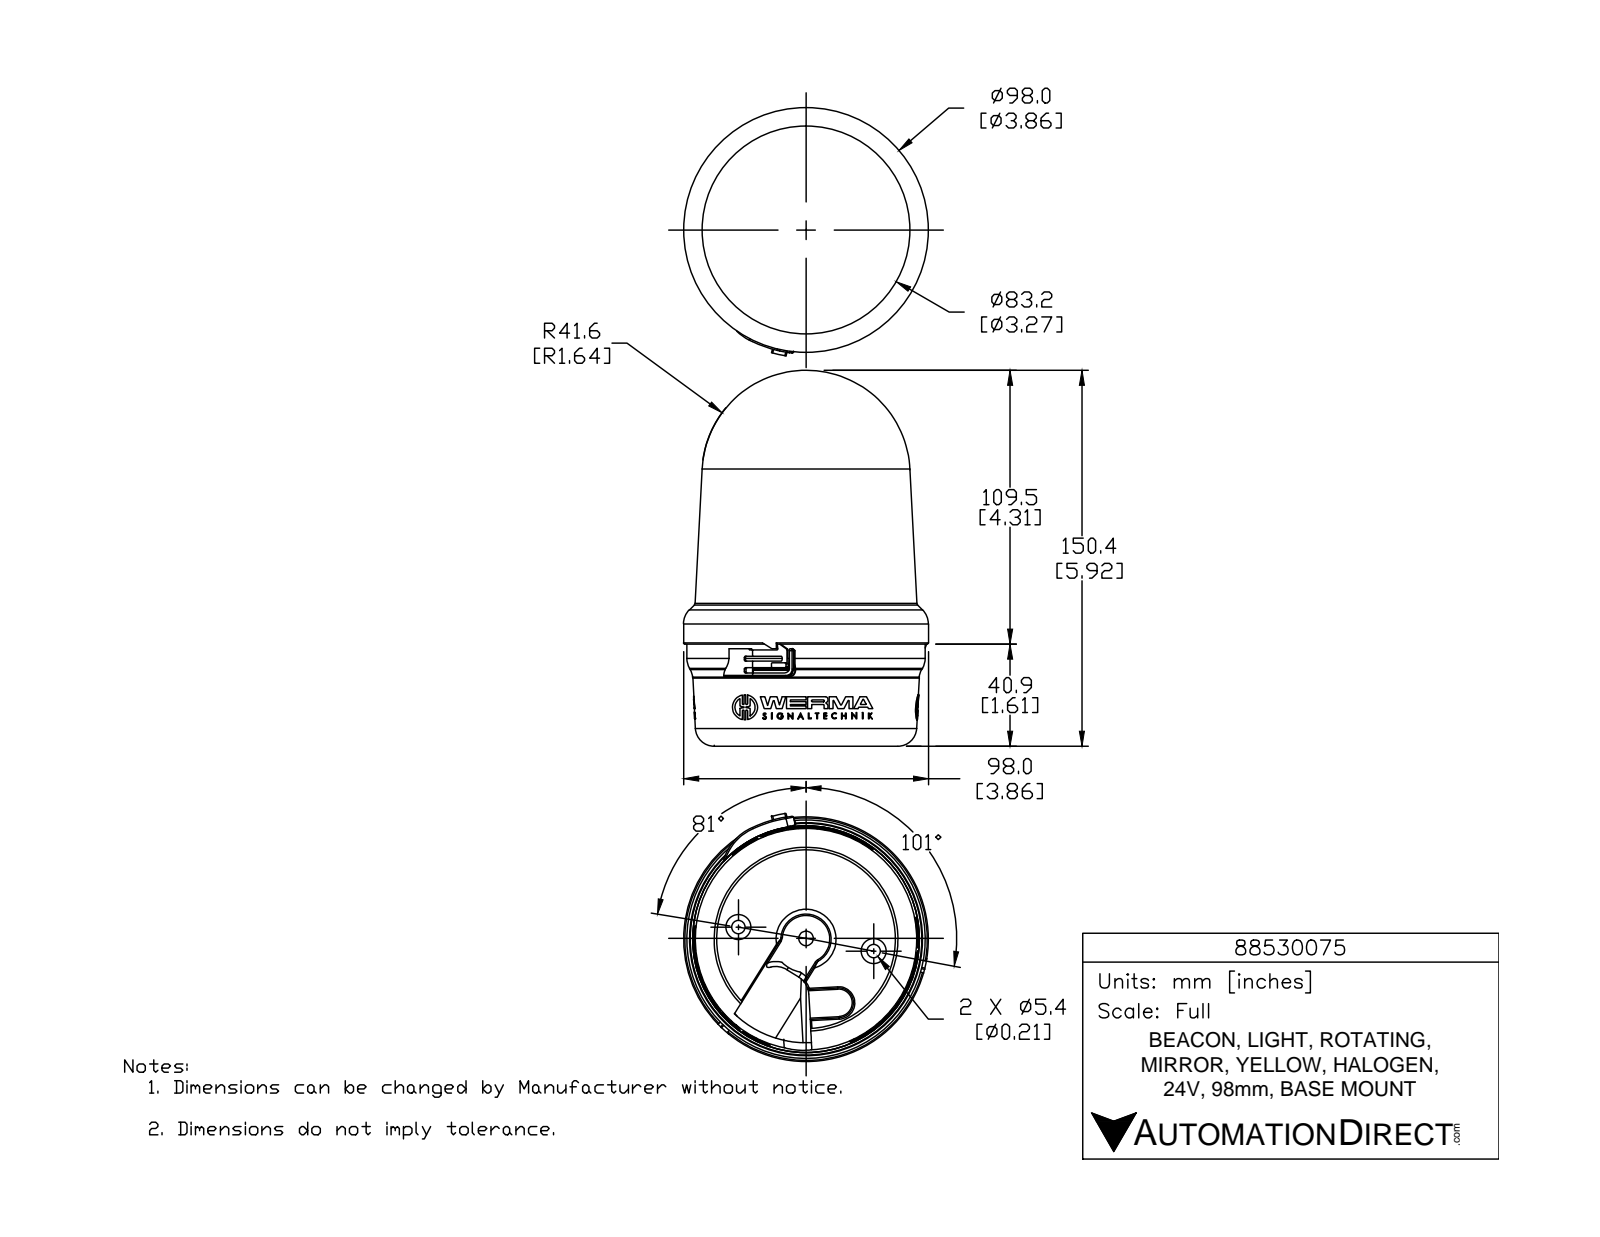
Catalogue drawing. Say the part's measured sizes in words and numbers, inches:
The part is named "88530075". Its 3-D file was written by "SolidWorks 2015 (AUTOMOTIVE_DESIGN)". It is 1 solid with 969 faces: 586 planar, 238 cylindrical and 145 other. Overall it measures 5.921 by 3.912 by 3.858 inches. Its volume is 49.51 cubic inches and its surface area 82.1 square inches. Round holes: 3 of diameter 0.068, 2 of diameter 0.213, 2 of diameter 0.409, 1 of diameter 2.815. Round bosses or shafts: 3 of diameter 0.395, 3 of diameter 0.099, 2 of diameter 0.394, 1 of diameter 3.858, 1 of diameter 3.756, 1 of diameter 3.571. Partial cylindrical surfaces (rounded edges, fillets, slot ends): 21 of radius 0.02, 9 of radius 0.006, 6 of radius 0.006, 6 of radius 0.014, 6 of radius 0.014, 6 of radius 0.014, 6 of radius 0.229, 4 of radius 0.079. The main face-to-face distances are 0.059, 0.033, 0.27, 0.02, 0.289, 0.734, 0.768, 0.315, 1.319, 1.26. The hole center spacings are 1.083, 2.165.
